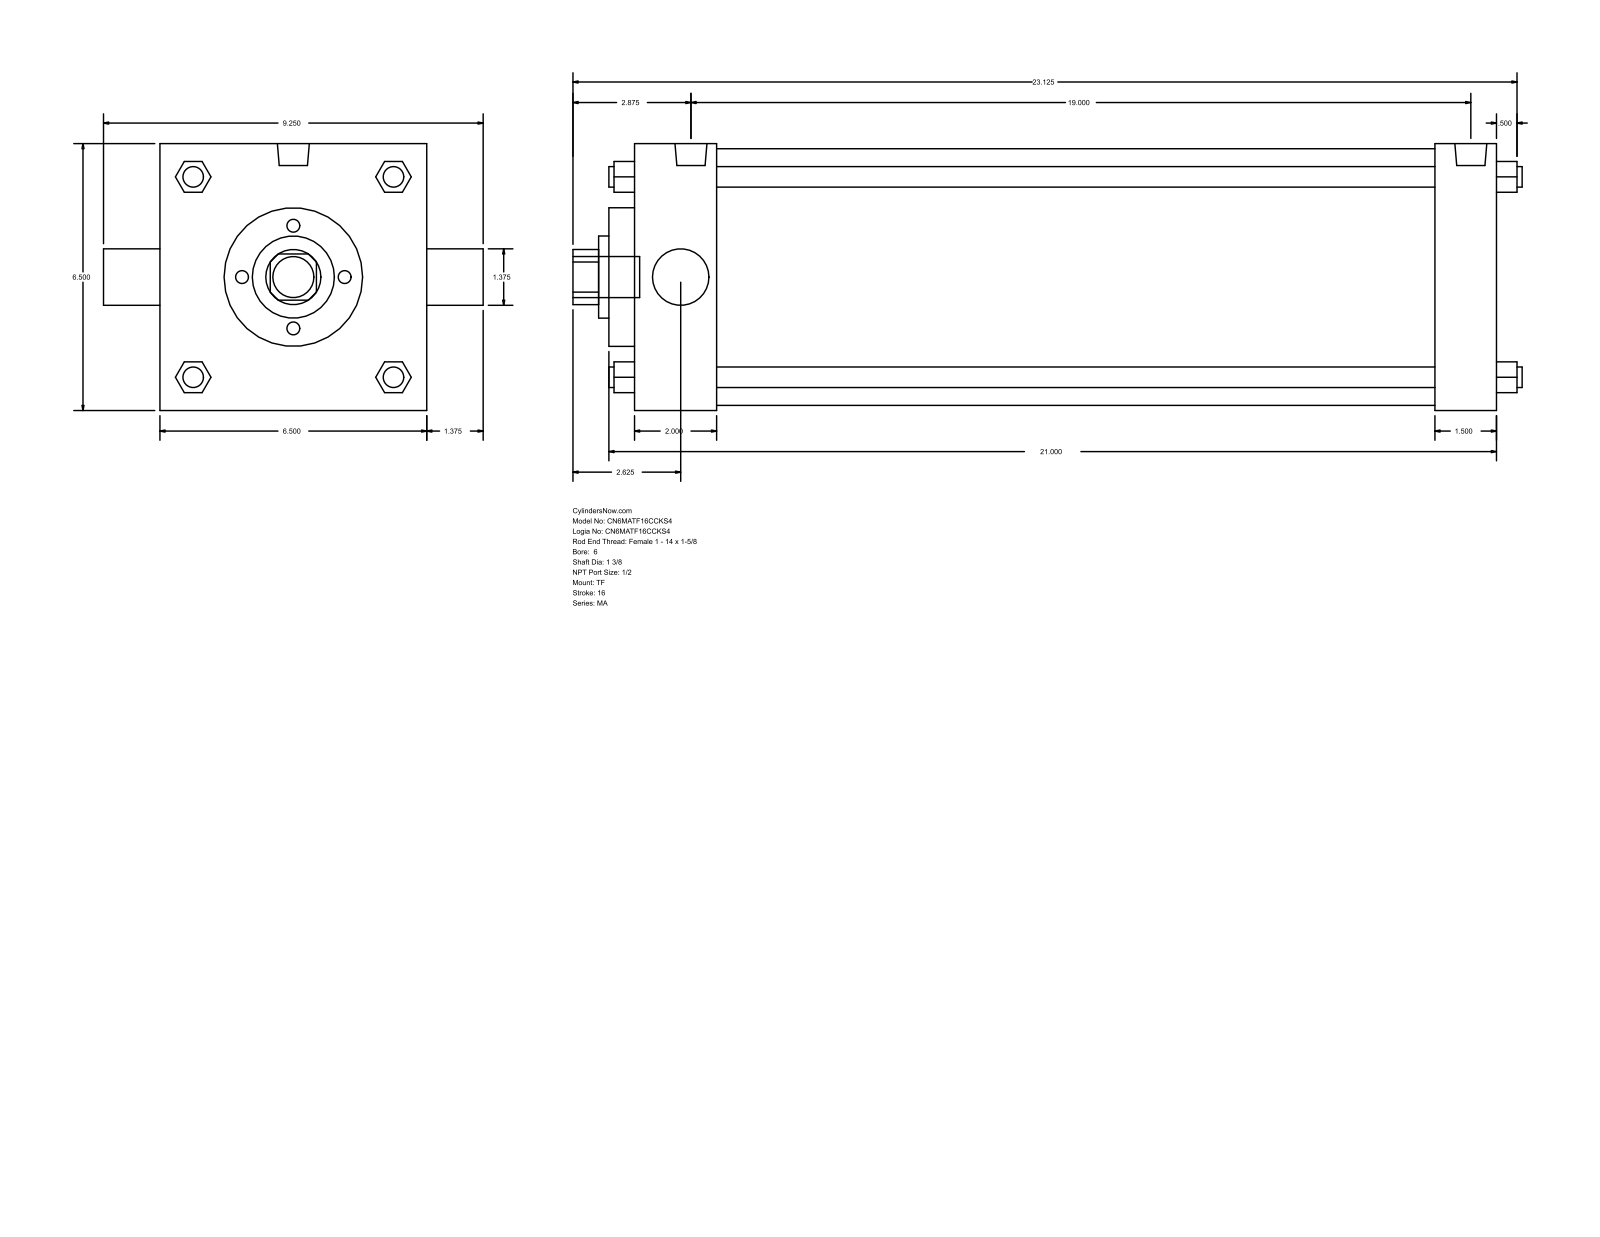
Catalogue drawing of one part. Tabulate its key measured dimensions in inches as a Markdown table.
| quantity | value |
| --- | --- |
| part name | MA_TF__0600_1.375 |
| STEP written by | GSSL Pune (CONFIG_CONTROL_DESIGN) |
| units | inches |
| bodies | 0 solids, 122 faces (93 planar, 29 cylindrical, 0 other) |
| overall size | 23.125 × 9.25 × 6.5 |
| round holes (diameter × count) | 1.375 × 2, 2 × 1, 3.375 × 1, 6.25 × 1 |
| round bosses / shafts (diameter × count) | 0.5 × 4, 0.687 × 3, 0.778 × 2, 1 × 1 |
| partial cylindrical surfaces (radius × count) | 0.672 × 1 |
| main face-to-face distances | 6.5, 21.125, 2, 19.625, 19.125, 17.625, 1.5, 0.625, 2.625, 20.25 |
